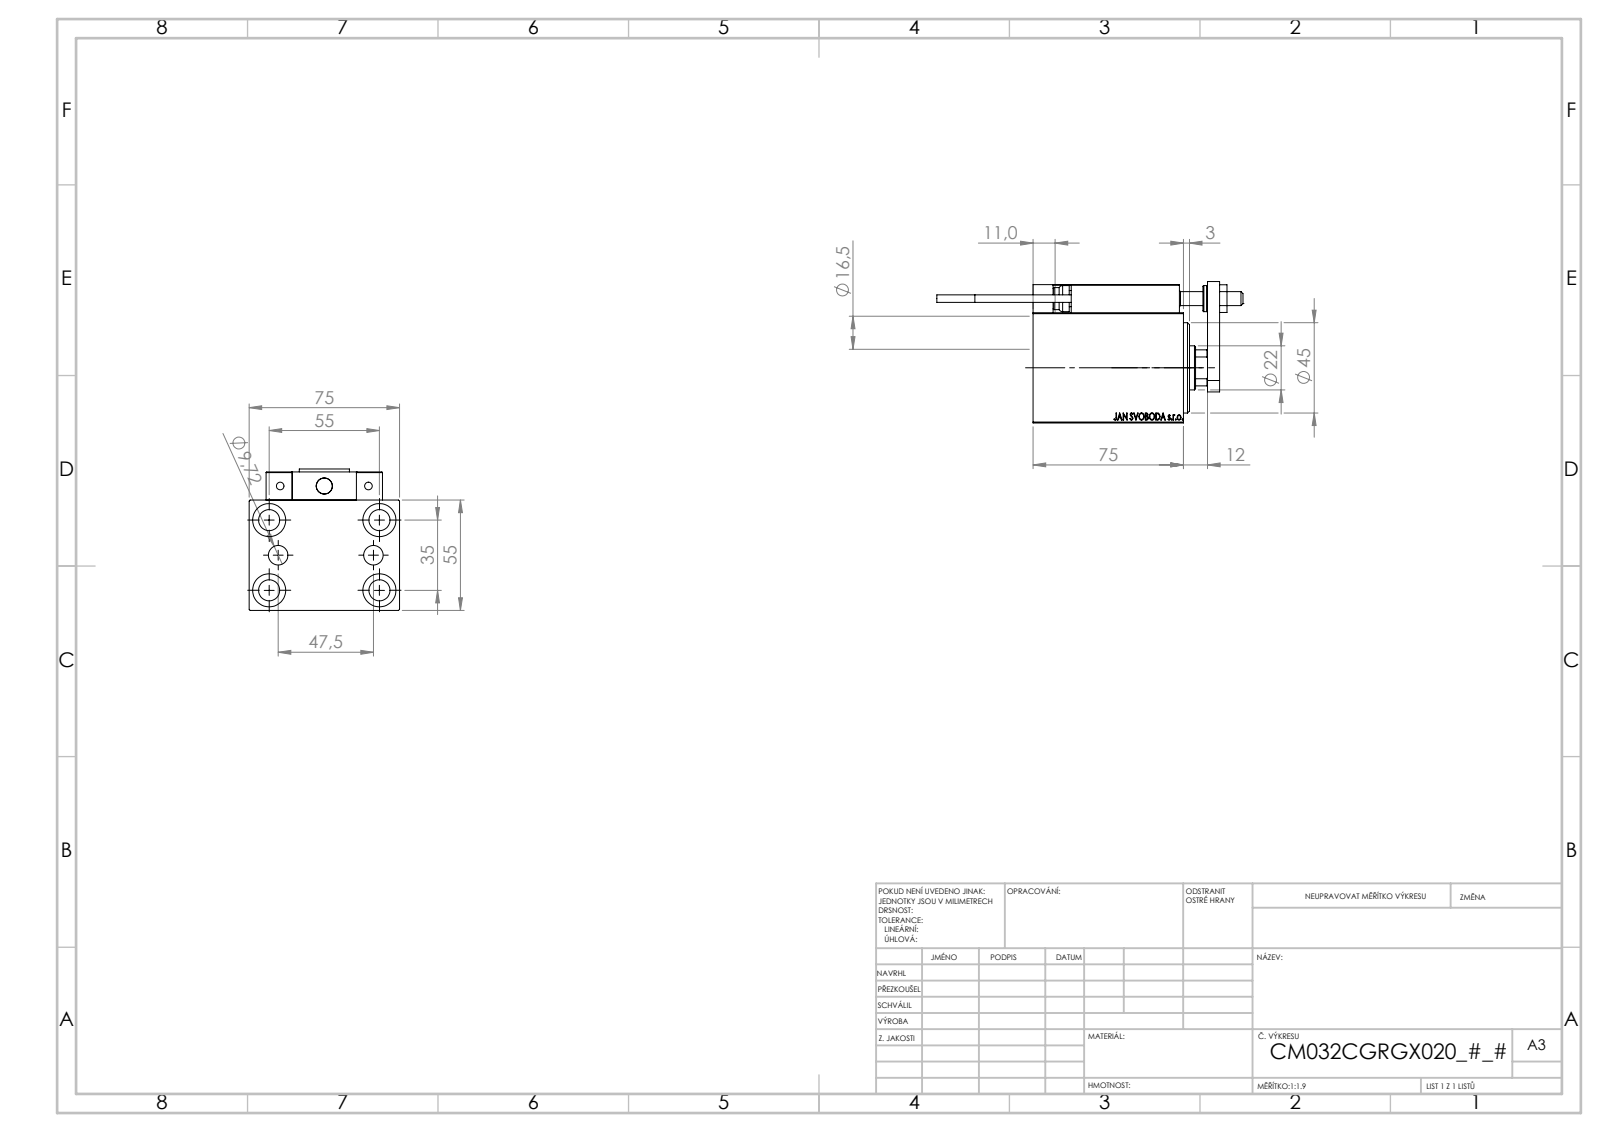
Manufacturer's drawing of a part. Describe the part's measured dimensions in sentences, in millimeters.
The part is named "SWITCH DIM B,W; MAGNET; Block; V450CM_C_VCP (+7 more)". Its 3-D file was written by "SolidWorks 2019 (CONFIG_CONTROL_DESIGN)". It is 23 solids with 1278 faces: 560 planar, 184 cylindrical and 534 other. Overall it measures 152.7 by 75 by 70.5 millimeters. Its volume is 314 003 cubic millimeters and its surface area 87 267 square millimeters. Round holes: 6 of diameter 4, 5 of diameter 8, 5 of diameter 10.5, 5 of diameter 16.5, 4 of diameter 3.2, 2 of diameter 5, 2 of diameter 9.72, 1 of diameter 7, 1 of diameter 22, 1 of diameter 25.5, 1 of diameter 32, 1 of diameter 34. Round bosses or shafts: 2 of diameter 5, 2 of diameter 3.8, 1 of diameter 13, 1 of diameter 11. Partial cylindrical surfaces (rounded edges, fillets, slot ends): 30 of radius 0.3, 2 of radius 3, 1 of radius 10.5. The main face-to-face distances are 55, 75, 14, 10, 69, 20, 25, 12, 5, 18. The hole center spacings are 17.9, 32.6, 54.16, 11.37, 20, 23.75, 27.07, 29.59.
